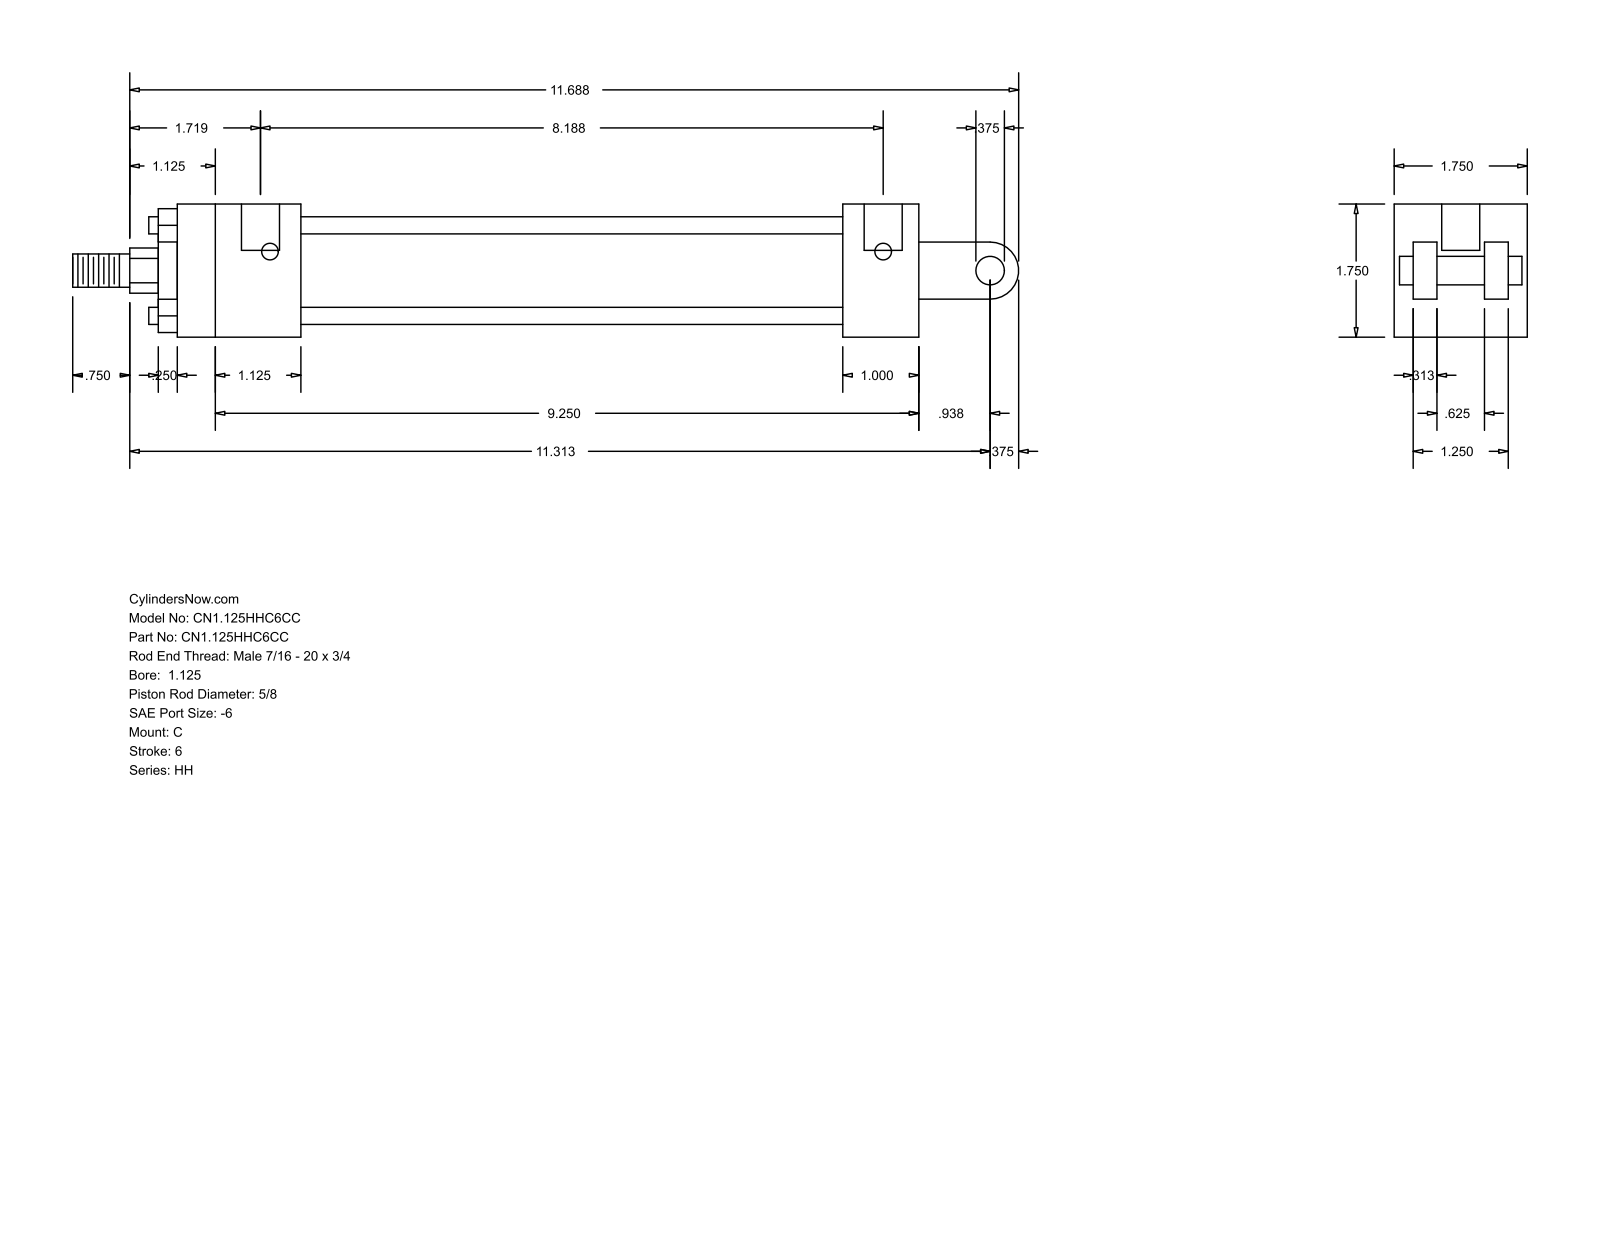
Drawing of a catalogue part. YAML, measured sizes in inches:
part_name: "HH_C__0112_0.625"
step_written_by: "GSSL Pune (CONFIG_CONTROL_DESIGN)"
units: inches
bodies: {solids: 0, faces: 99, planar: 70, cylindrical: 29, other: 0}
overall_size: [12.437, 1.75, 1.75]
round_holes:
  - {diameter: 0.219, count: 4}
  - {diameter: 0.5, count: 2}
round_bosses_or_shafts:
  - {diameter: 0.225, count: 4}
  - {diameter: 1.375, count: 1}
  - {diameter: 1.125, count: 1}
  - {diameter: 0.625, count: 1}
  - {diameter: 0.437, count: 1}
  - {diameter: 0.375, count: 1}
partial_cylinders:
  - {radius: 0.297, count: 1}
  - {radius: 0.375, count: 1}
face_to_face_distances: [1.75, 0.25, 1.25, 0.563, 1, 1.188, 1.5, 0.313, 0.938, 0.5]
hole_center_spacings: [8.063, 0.125, 8.187]
